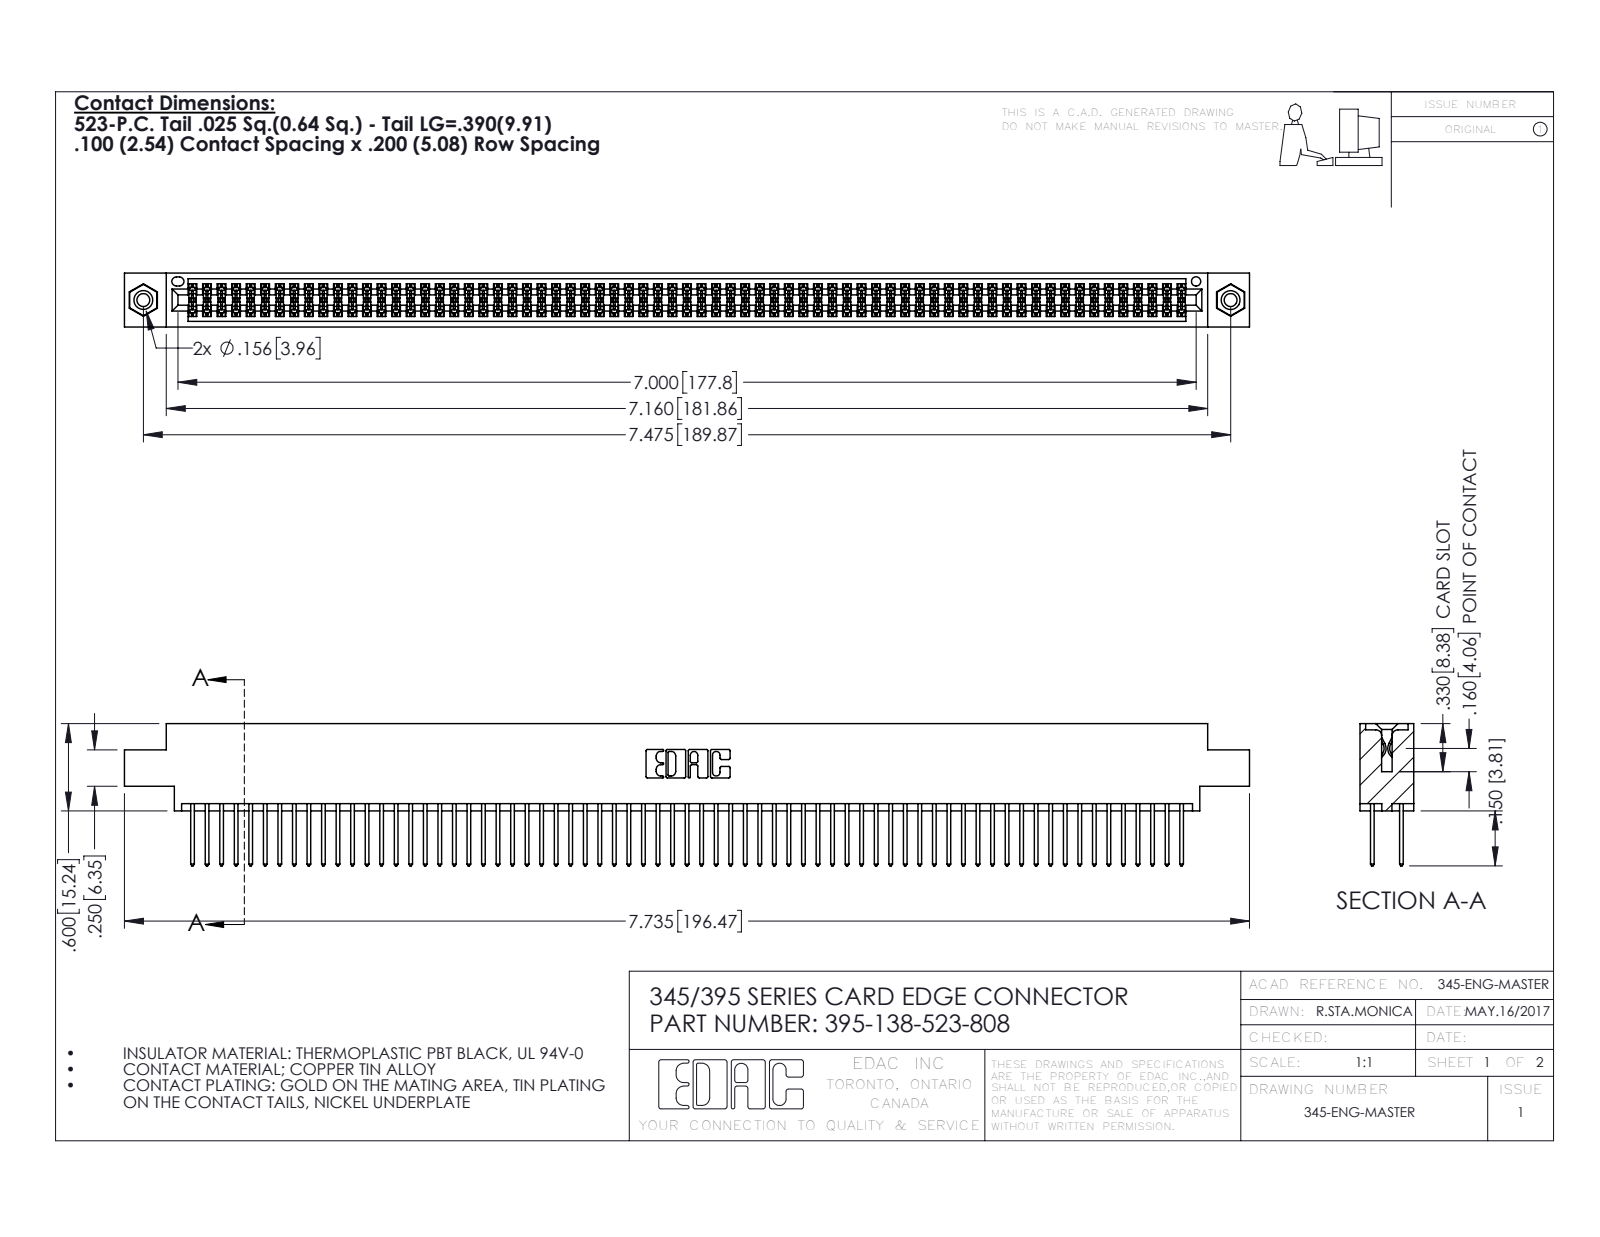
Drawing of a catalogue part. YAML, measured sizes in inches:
part_name: "345-292-001_345-293-123; 345 Part_0.170 Offset - 0.156 Dia-TI; 345-250-001_345-250-003-102; 395-138-523-808"
step_written_by: "SolidWorks 2016 (CONFIG_CONTROL_DESIGN)"
units: inches
bodies: {solids: 141, faces: 7090, planar: 4670, cylindrical: 2404, other: 16}
overall_size: [7.735, 0.977, 0.37]
volume: 1.19
surface_area: 47.7
round_holes:
  - {diameter: 0.089, count: 2}
  - {diameter: 0.125, count: 2}
  - {diameter: 0.156, count: 2}
  - {diameter: 0.064, count: 1}
round_bosses_or_shafts:
  - {diameter: 0.155, count: 2}
partial_cylinders:
  - {radius: 0.006, count: 207}
  - {radius: 0.01, count: 138}
  - {radius: 0.01, count: 22}
  - {radius: 0.007, count: 6}
  - {radius: 0.031, count: 6}
  - {radius: 0.026, count: 3}
  - {radius: 0.014, count: 2}
  - {radius: 0.019, count: 2}
face_to_face_distances: [0.072, 0.298, 0.2, 0.098, 0.272, 0.025, 0.37, 0.225, 0.175, 0.149]
hole_center_spacings: [0.27, 7.239, 7.475]
